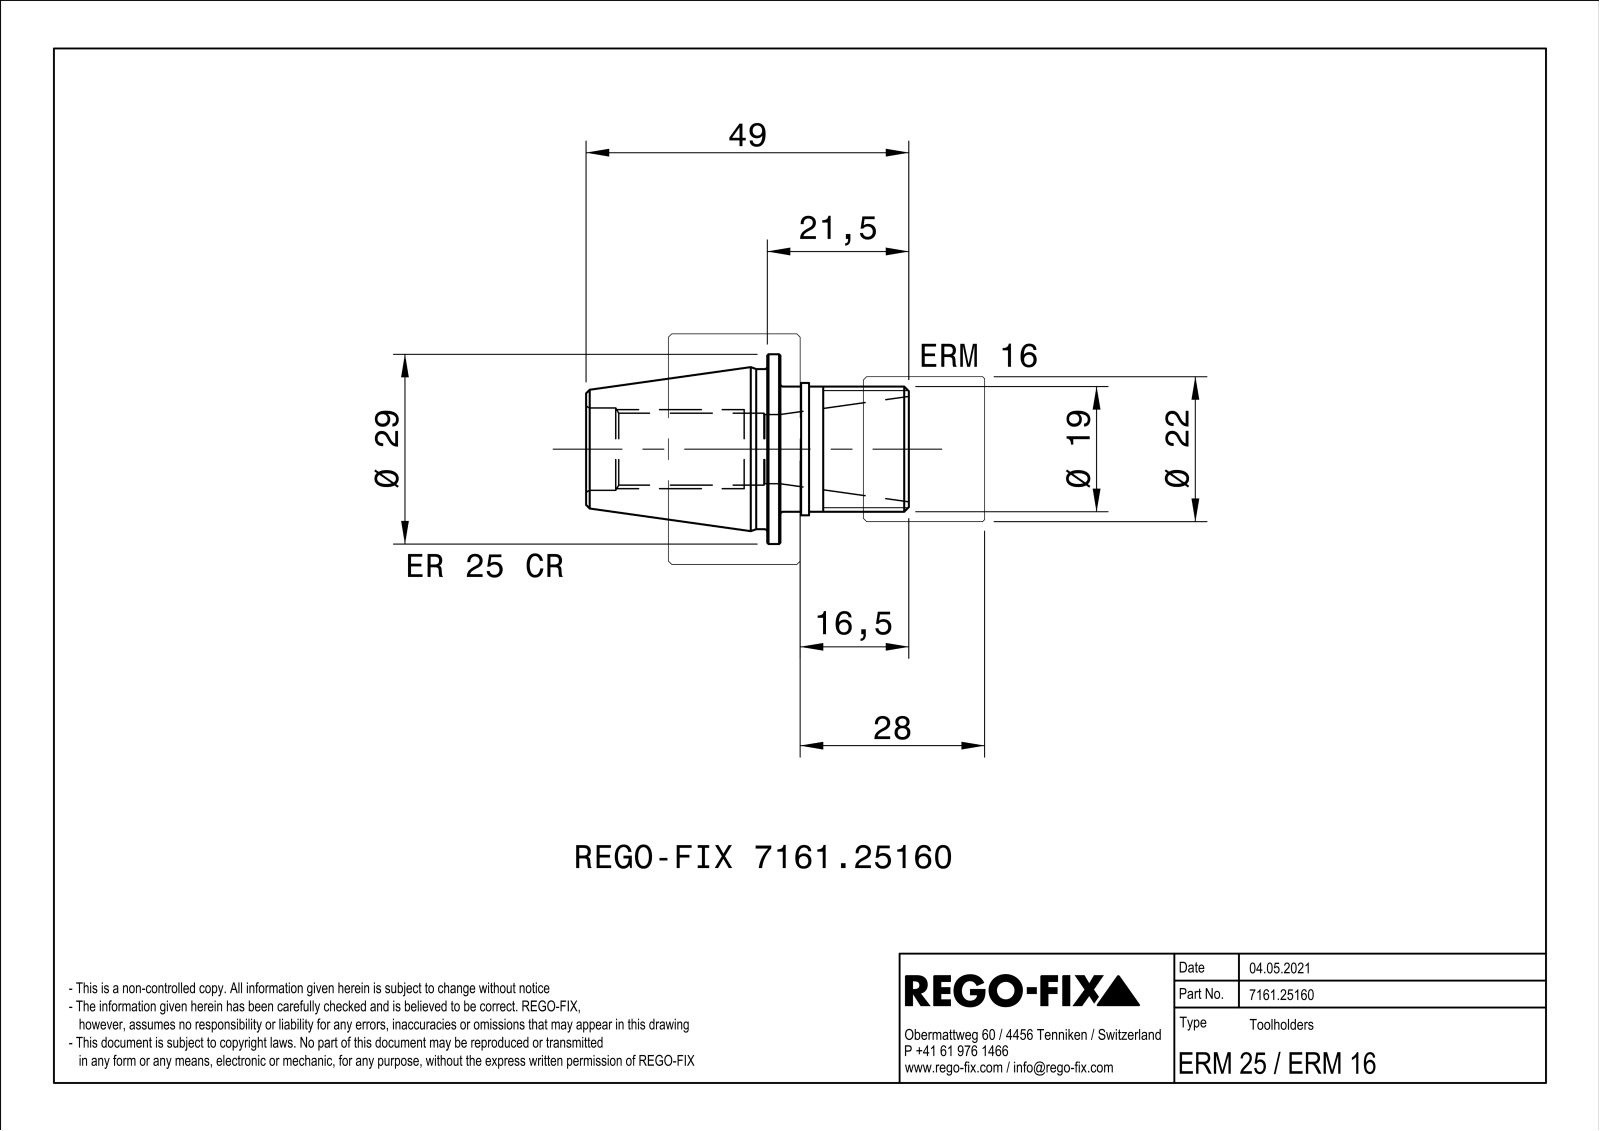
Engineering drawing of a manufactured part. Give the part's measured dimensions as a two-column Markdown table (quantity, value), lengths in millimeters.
| quantity | value |
| --- | --- |
| part name | NOCUT |
| STEP written by | SIEMENS PLM Software Solid Edge ST10 (AUTOMOTIVE_DESIGN) |
| units | millimeters |
| bodies | 1 solid, 81 faces (37 planar, 17 cylindrical, 27 other) |
| overall size | 49 × 35 × 35 |
| volume | 16 624 mm³ |
| surface area | 9 481 mm² |
| round holes (diameter × count) | 10.5 × 1, 10.92 × 1, 12.5 × 1, 19.4 × 1, 28.92 × 1, 30.4 × 1 |
| round bosses / shafts (diameter × count) | 35 × 1, 28.8 × 1, 24.3 × 1, 23.2 × 1, 19 × 1, 17.9 × 1, 10 × 1 |
| partial cylindrical surfaces (radius × count) | 6 × 2 |
| main face-to-face distances | 5, 8, 13, 13.15, 1.2, 1.35, 14.35, 6.35, 5.15, 12.5 |
